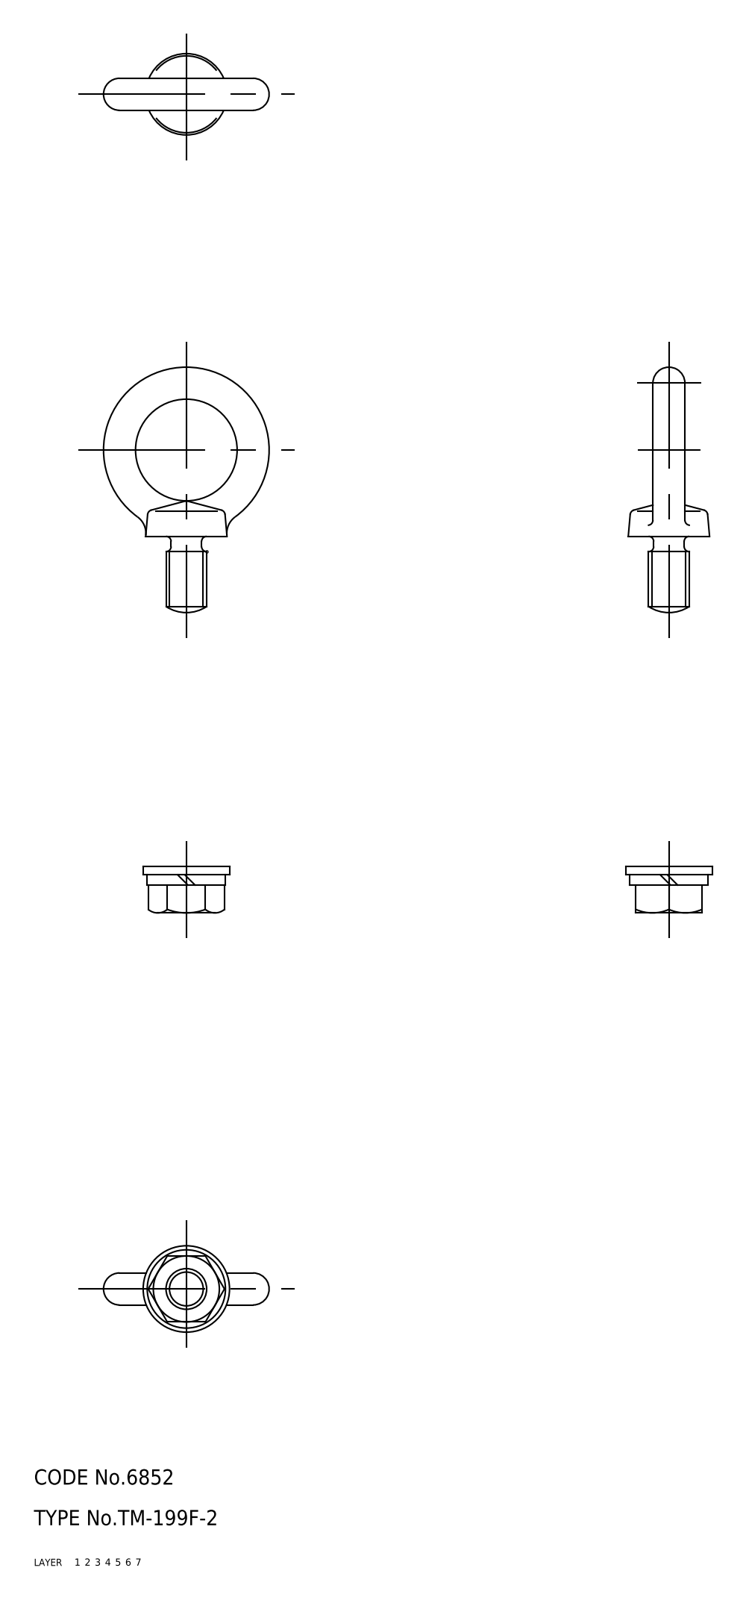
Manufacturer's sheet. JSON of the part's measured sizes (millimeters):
{"part_name": "TM_199F_2", "step_written_by": "SolidWorks 2003240 (AUTOMOTIVE_DESIGN)", "units": "millimeters", "bodies": {"solids": 4, "faces": 52, "planar": 13, "cylindrical": 12, "other": 27}, "overall_size": [48.3, 32.6, 17], "volume_mm3": 5119, "surface_area_mm2": 3778, "round_holes": [[8, 1]], "round_bosses_or_shafts": [[17, 1], [15.4, 1]], "face_to_face_distances": [1.6, 2, 3.6, 13, 5.5, 7.5, 9.1]}
